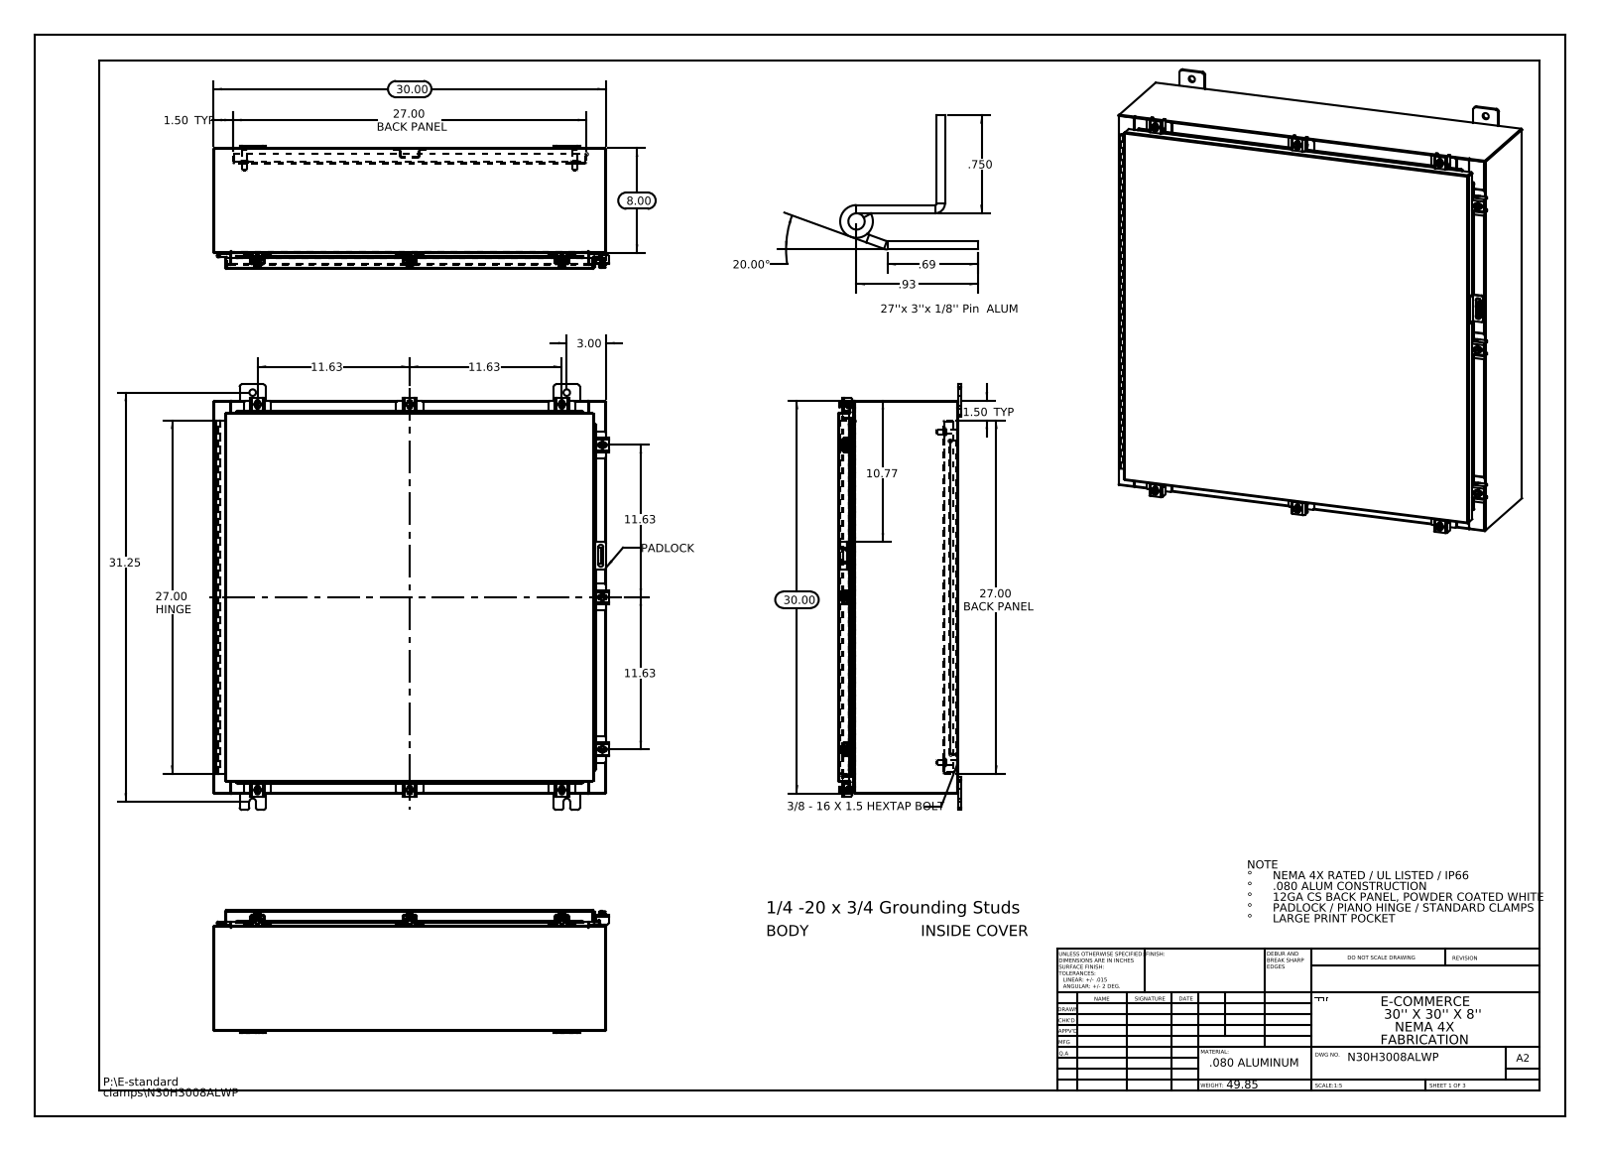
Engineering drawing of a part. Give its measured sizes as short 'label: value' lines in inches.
name: N30H3008ALWP 125 Pin Hinge; N30H3008ALWP Padlock Hasp; N30H3008ALWP Mounting Feet; N30H3008ALWP Enclosure Stiffener (+8 more)
written by: SolidWorks 2013 (CONFIG_CONTROL_DESIGN)
unit: in
bodies: 63 solids, 2262 faces (1206 planar, 936 cylindrical, 120 other)
size: 32.5 × 30.211 × 9.389
volume: 325.9 in³; area: 8 130 in²
holes: 9× ⌀0.213, 9× ⌀0.26, 8× ⌀0.5, 2× ⌀0.125, 1× ⌀0.125
bosses: 10× ⌀0.25, 9× ⌀0.5, 9× ⌀0.399, 4× ⌀0.625, 4× ⌀0.375, 4× ⌀0.33
rounds: 42× R0.06, 31× R0.013, 25× R0.088, 24× R0.19, 18× R0.12, 18× R0.141, 13× R0.05, 12× R0.08
face distances: 0.075, 9.126, 29.925, 9.051, 9.201, 0.104, 1, 8.126, 1.075, 8.051
hole spacings: 2.326, 11.625, 12.798, 15.048, 27.369, 30.124, 31.663, 36.553
